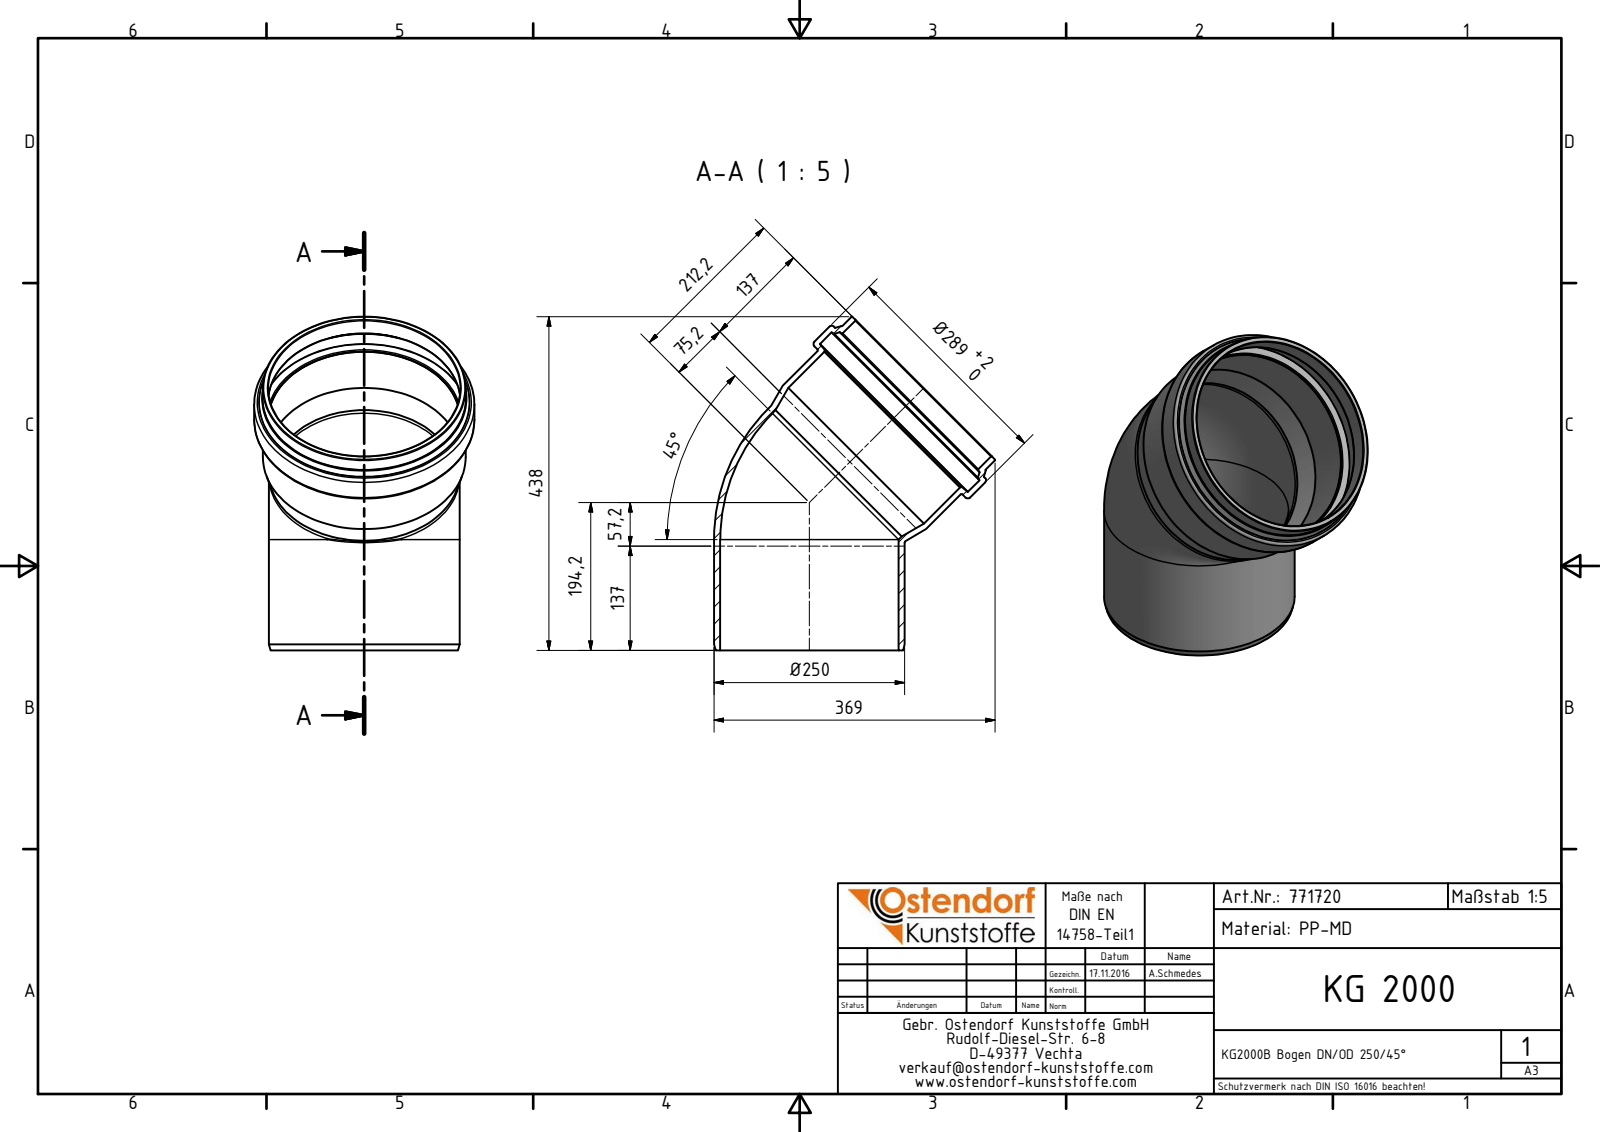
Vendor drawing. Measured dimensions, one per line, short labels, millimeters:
name: 771720 KG2000B Bogen DN_OD 250_45°
written by: Autodesk Inventor 2016 (AUTOMOTIVE_DESIGN)
unit: mm
bodies: 1 solid, 41 faces (5 planar, 11 cylindrical, 25 other)
size: 438 × 369 × 289
volume: 2 394 000 mm³; area: 669 176 mm²
holes: 2× ⌀234.3, 2× ⌀252.1, 1× ⌀251.7, 1× ⌀274.6
bosses: 2× ⌀250.3, 1× ⌀289, 1× ⌀266.5, 1× ⌀266.1
face distances: 62.59, 36.3, 26.29, 4.22, 32.08, 58.37
